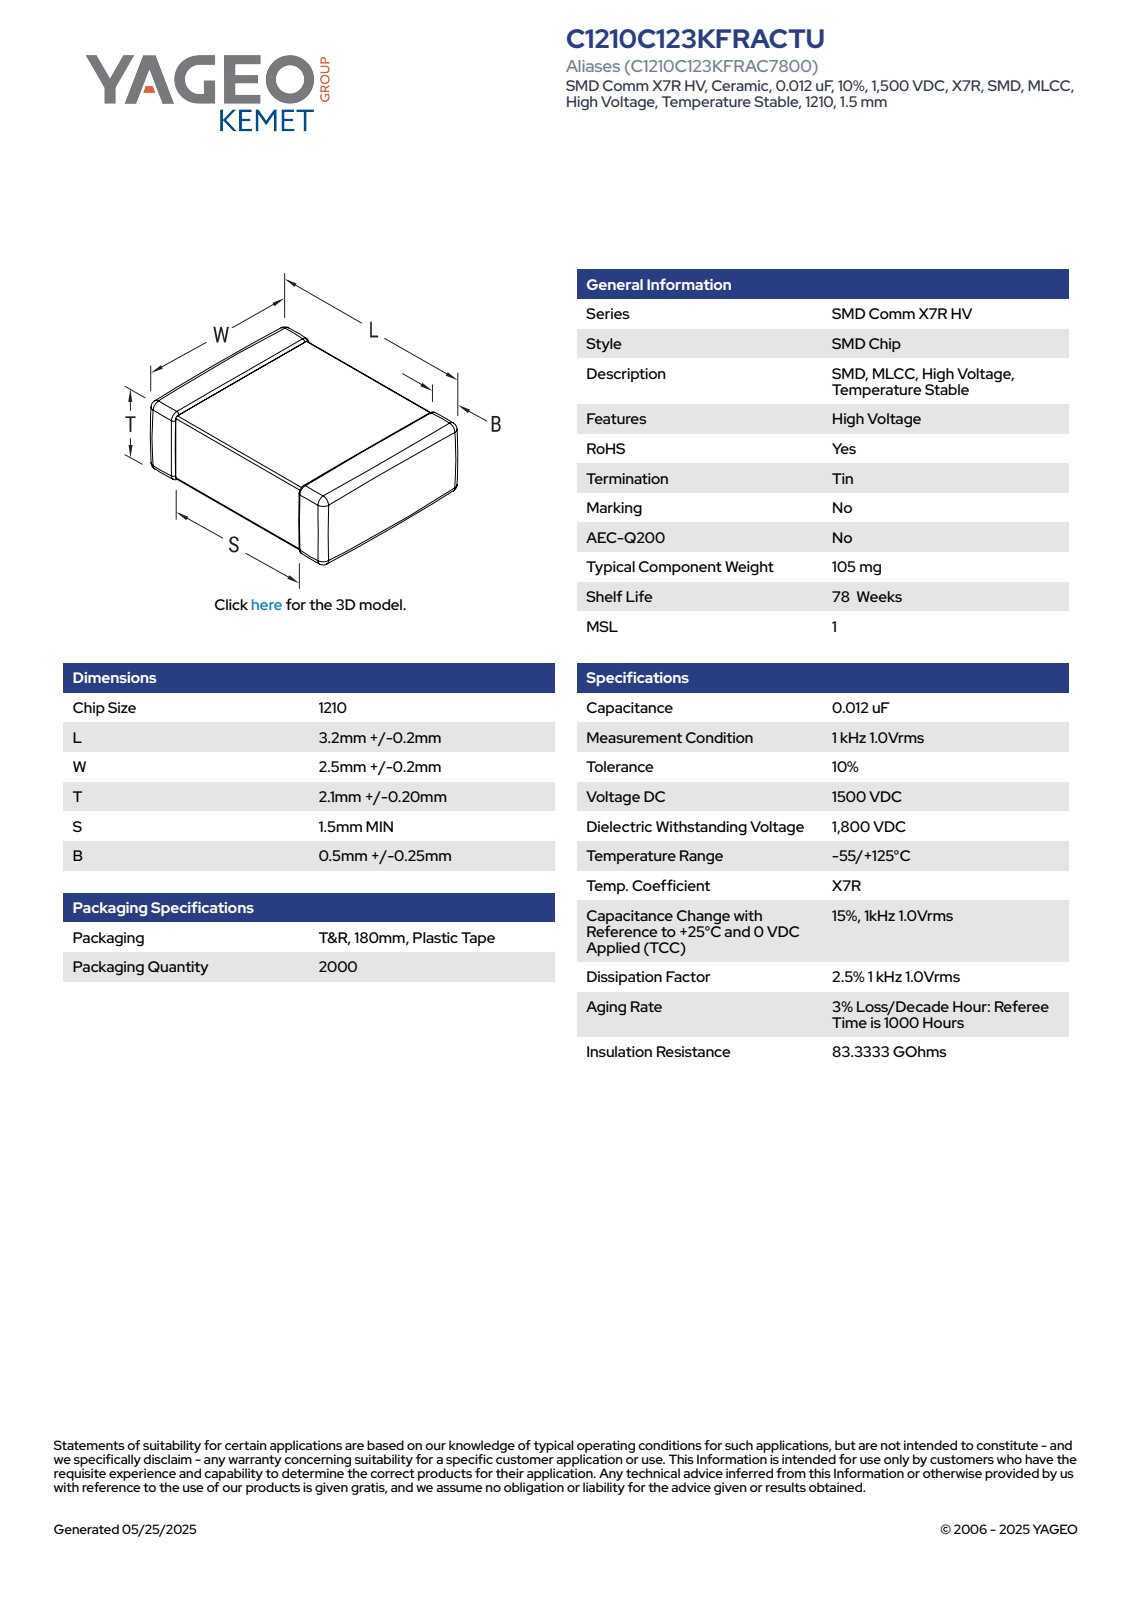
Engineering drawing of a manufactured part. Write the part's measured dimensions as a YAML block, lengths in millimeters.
part_name: "CCS_CCSTDNOS_1210_L3.4W2.7T2.3B0.75"
step_written_by: "SolidWorks 2014 (AUTOMOTIVE_DESIGN)"
units: millimeters
bodies: {solids: 4, faces: 125, planar: 71, cylindrical: 38, other: 16}
overall_size: [3.4, 2.7, 2.3]
volume: 20
surface_area: 46
face_to_face_distances: [2.24, 3.4, 2.64, 2.18, 2.58, 2.3, 2.7, 2.25, 2.19, 1.31]
